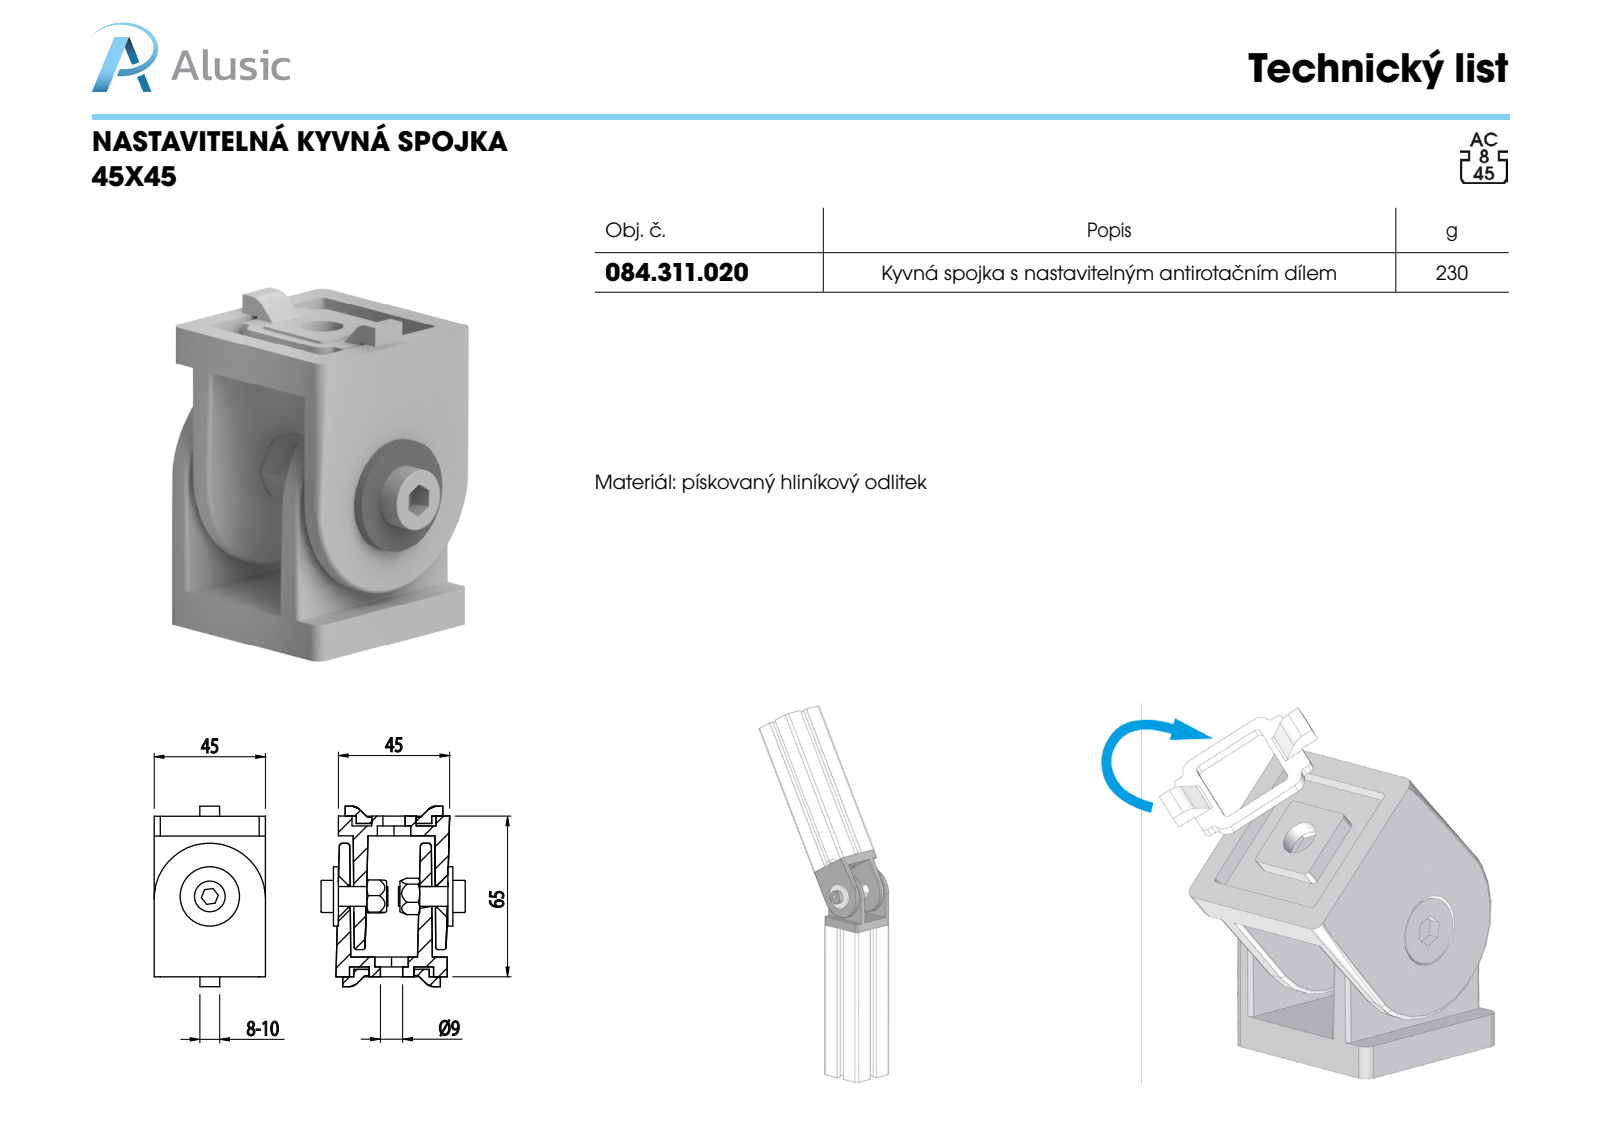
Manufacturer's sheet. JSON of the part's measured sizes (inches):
{"part_name": "084.311.020; torque nut 03_iso_ISO 7042-M8-N; plain washer large grade ac_iso_Washer ISO 7093 - 10; serrated lock washer 2_din_DIN 6798-V10.5 (+3 more)", "step_written_by": "SolidWorks 2012 (CONFIG_CONTROL_DESIGN)", "units": "inches", "bodies": {"solids": 11, "faces": 436, "planar": 268, "cylindrical": 96, "other": 72}, "overall_size": [2.725, 2.295, 1.912], "volume_in3": 4.165, "surface_area_in2": 56.64, "round_holes": [[0.354, 3], [0.268, 1], [0.315, 1], [0.331, 1]], "round_bosses_or_shafts": [[0.945, 1], [0.512, 1]], "partial_cylinders_radius": [[0.039, 38], [0.098, 8], [0.118, 4], [0.157, 2], [0.886, 2]], "face_to_face_distances": [0.157, 0.315, 1.291, 1.291, 1.3, 1.3, 0.315, 0.079, 0.157, 1.823]}
